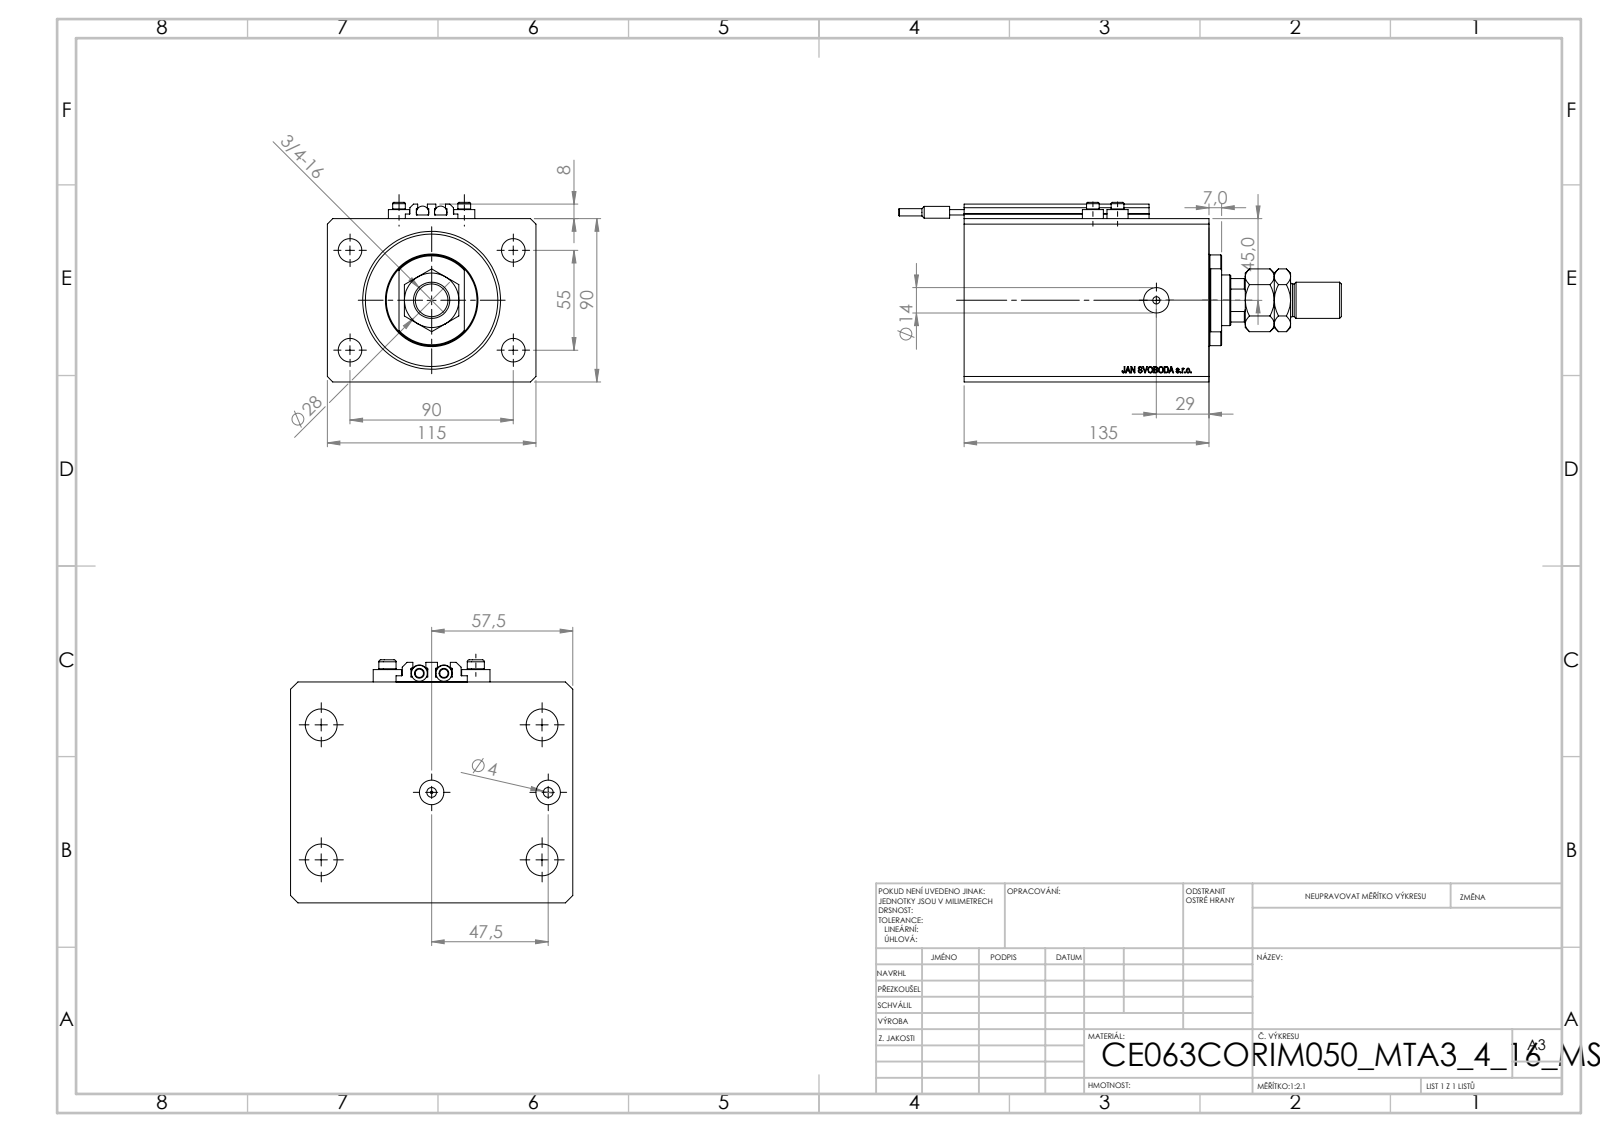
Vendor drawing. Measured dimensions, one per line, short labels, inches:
name: V250CE_VC_C; SWITCH_V250CE; ALLEN BOLT V250CE; MTA (+2 more)
written by: SolidWorks 2019 (CONFIG_CONTROL_DESIGN)
unit: in
bodies: 11 solids, 1139 faces (551 planar, 104 cylindrical, 484 other)
size: 9.602 × 4.528 × 3.898
volume: 76.34 in³; area: 291.2 in²
holes: 8× ⌀0.157, 4× ⌀0.512, 2× ⌀0.394, 2× ⌀0.551, 1× ⌀0.049, 1× ⌀0.728, 1× ⌀1.102, 1× ⌀2.48, 1× ⌀2.992
bosses: 4× ⌀0.457, 4× ⌀0.276, 2× ⌀0.268, 2× ⌀0.256, 2× ⌀0.157, 1× ⌀1.969, 1× ⌀0.787, 1× ⌀0.709
rounds: 10× R0.008, 1× R0.531
face distances: 3.543, 4.528, 5.315, 0.705, 4.61, 1.185, 3.425, 4.13, 1.969, 0.118
hole spacings: 2.076, 0.535, 1.087, 1.417, 1.515, 2.165, 3.543, 3.799
